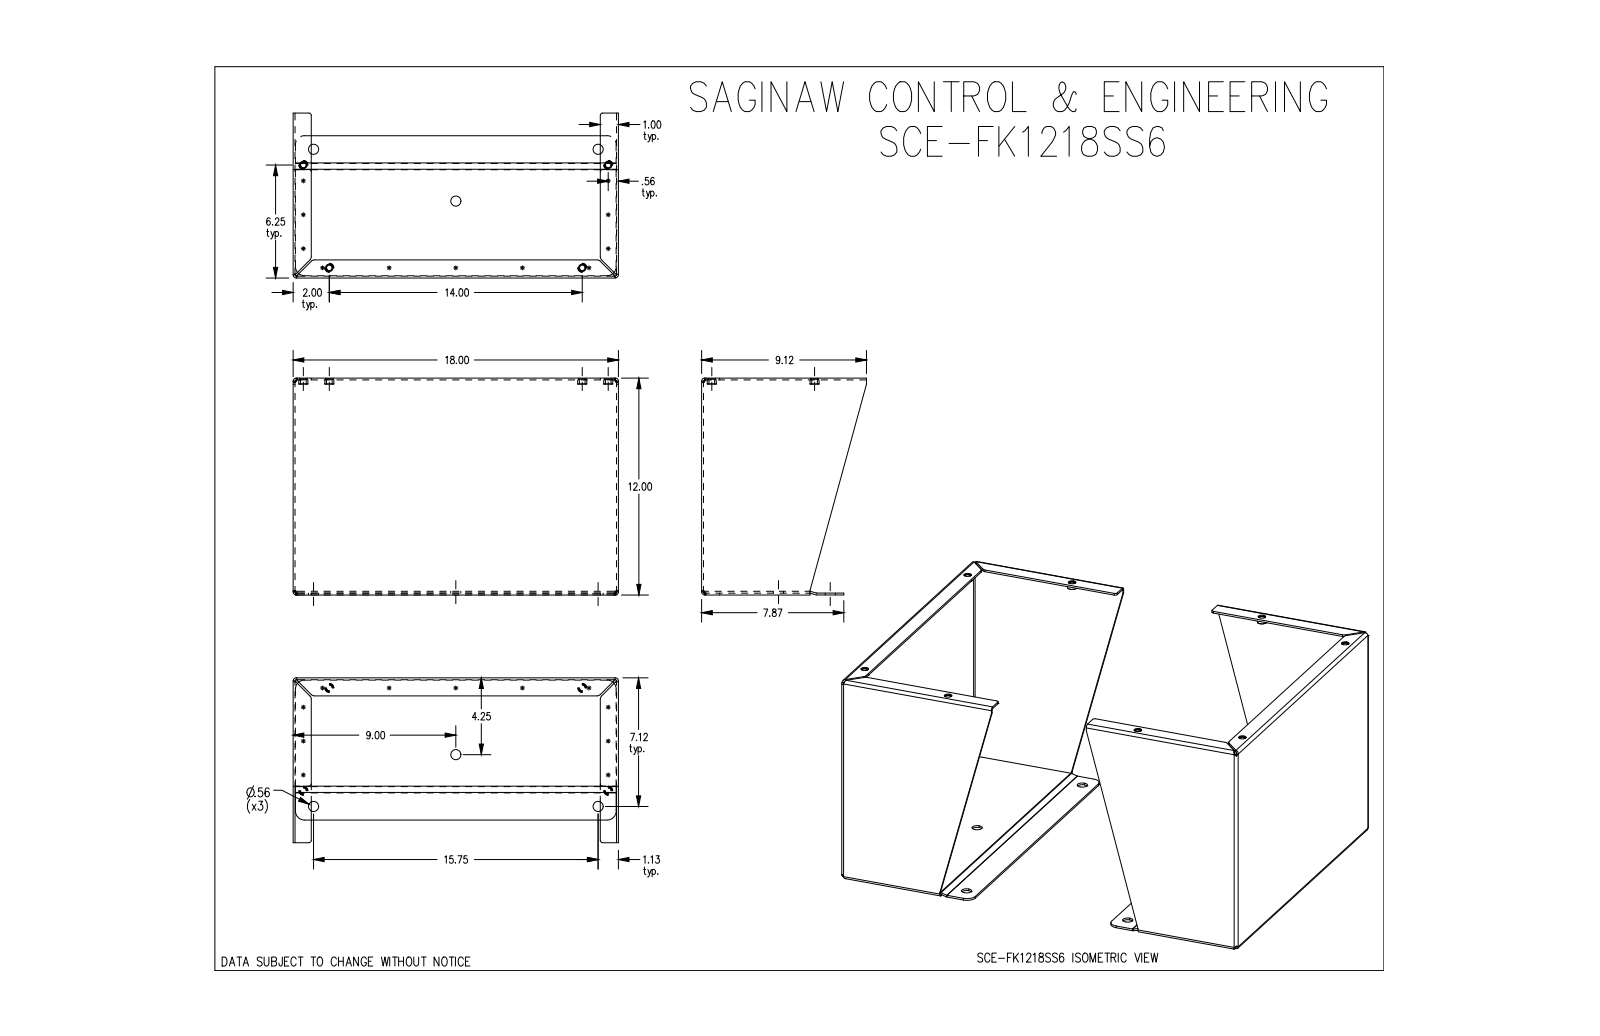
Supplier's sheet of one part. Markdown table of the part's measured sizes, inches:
| quantity | value |
| --- | --- |
| part name | SCE-FK1218SS6 |
| STEP written by | SolidWorks 2019 (CONFIG_CONTROL_DESIGN) |
| units | inches |
| bodies | 12 solids, 286 faces (120 planar, 110 cylindrical, 56 other) |
| overall size | 24 × 18 × 12 |
| volume | 121.2 in³ |
| surface area | 2 367 in² |
| round holes (diameter × count) | 0.312 × 8, 0.413 × 8, 0.563 × 6 |
| round bosses / shafts (diameter × count) | 0.5 × 8, 0.412 × 8 |
| partial cylindrical surfaces (radius × count) | 0.166 × 16, 0.062 × 12, 0.125 × 8, 0.22 × 8, 0.5 × 8, 0.063 × 6 |
| main face-to-face distances | 0.104, 23.896, 17.896, 23.792, 24, 18, 17.792, 11.792, 0.101, 11.893 |
| hole center spacings | 1.035, 5.866, 6.614, 7.913, 8.671, 10.646, 14.884, 15.919 |
